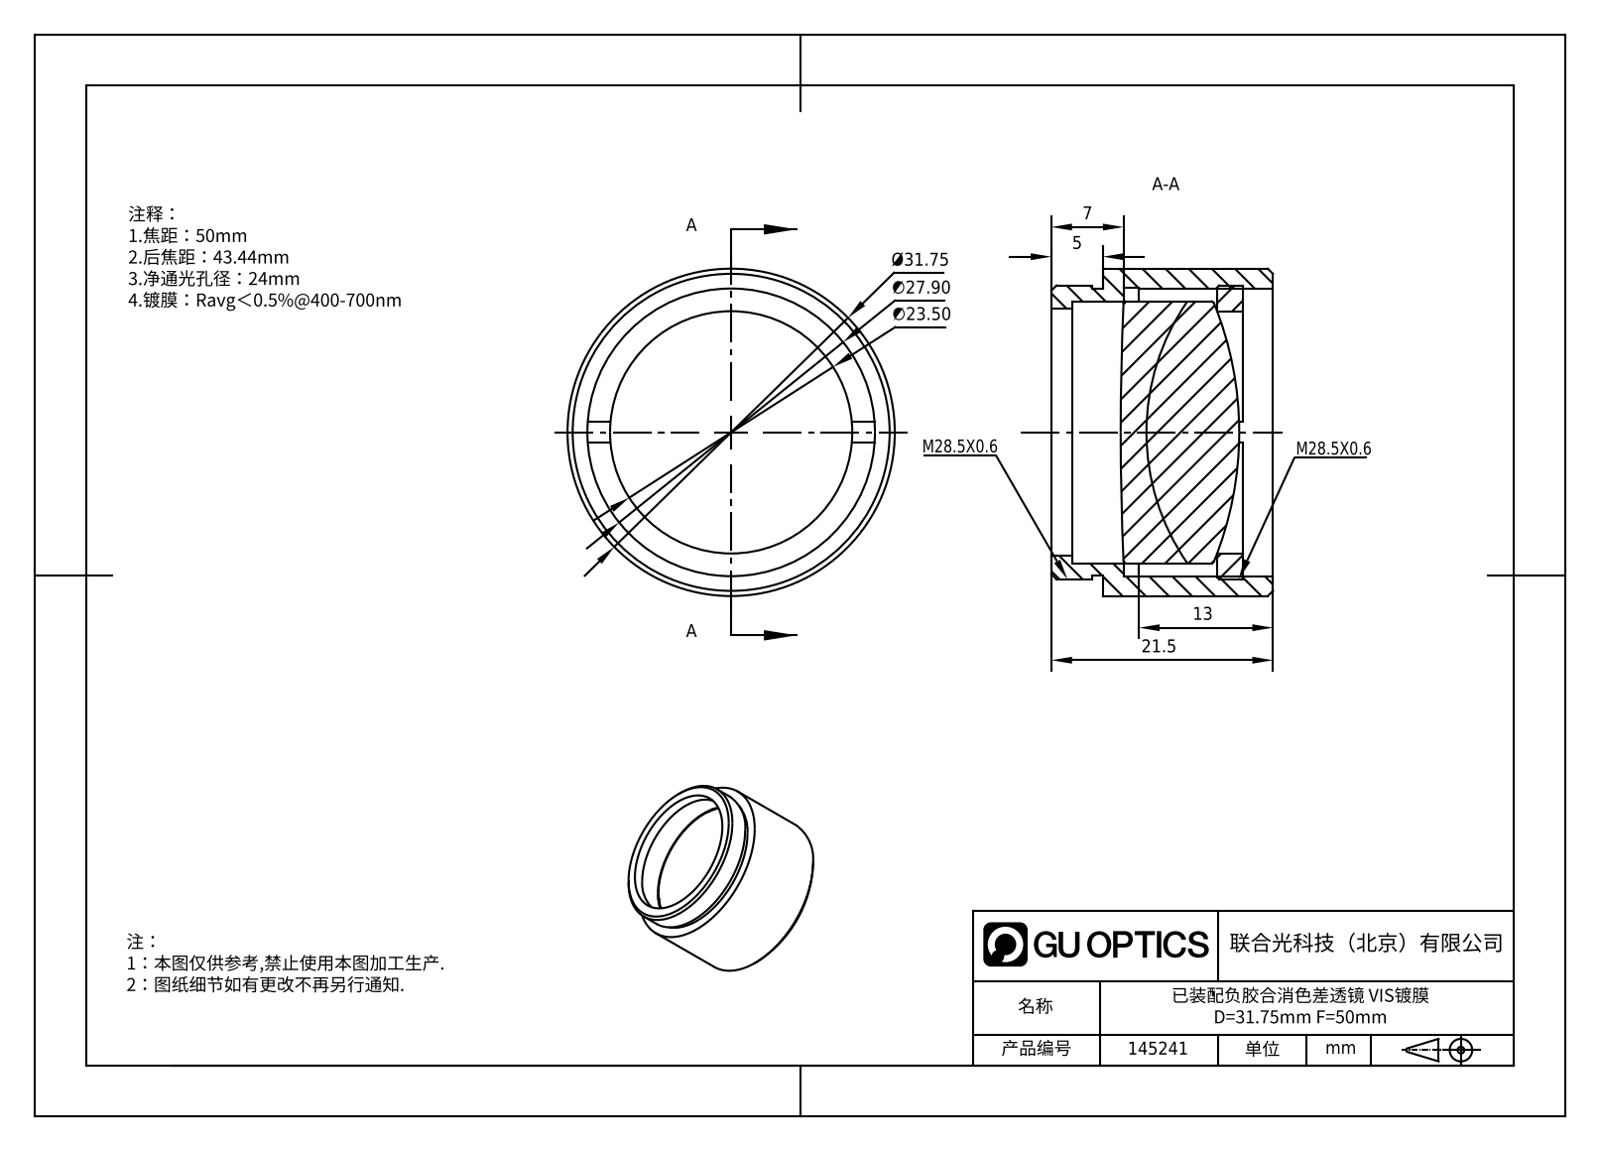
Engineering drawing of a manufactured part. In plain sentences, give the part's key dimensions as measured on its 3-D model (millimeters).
The part is named "M28.5x0.6安装环PN35021-LM254-D2; GL31-025B-050-VIS_Solidworks; M28.5x0.6ѹȦ; APD-ML25-050-VIS". Its 3-D file was written by "SolidWorks 2022 (AUTOMOTIVE_DESIGN)". It is 4 solids with 56 faces: 16 planar, 22 cylindrical and 18 other. Overall it measures 31.76 by 31.76 by 21.5 millimeters. Its volume is 9 518 cubic millimeters and its surface area 8 243 square millimeters. Round holes: 1 of diameter 23.5, 1 of diameter 24, 1 of diameter 27.9, 1 of diameter 28. Round bosses or shafts: 1 of diameter 31.76, 1 of diameter 28.5, 1 of diameter 27.8, 1 of diameter 25.4. The main face-to-face distances are 2, 5, 2.5, 11.08, 13.58, 16.08, 18.58, 21.5, 16.5, 5.42.
